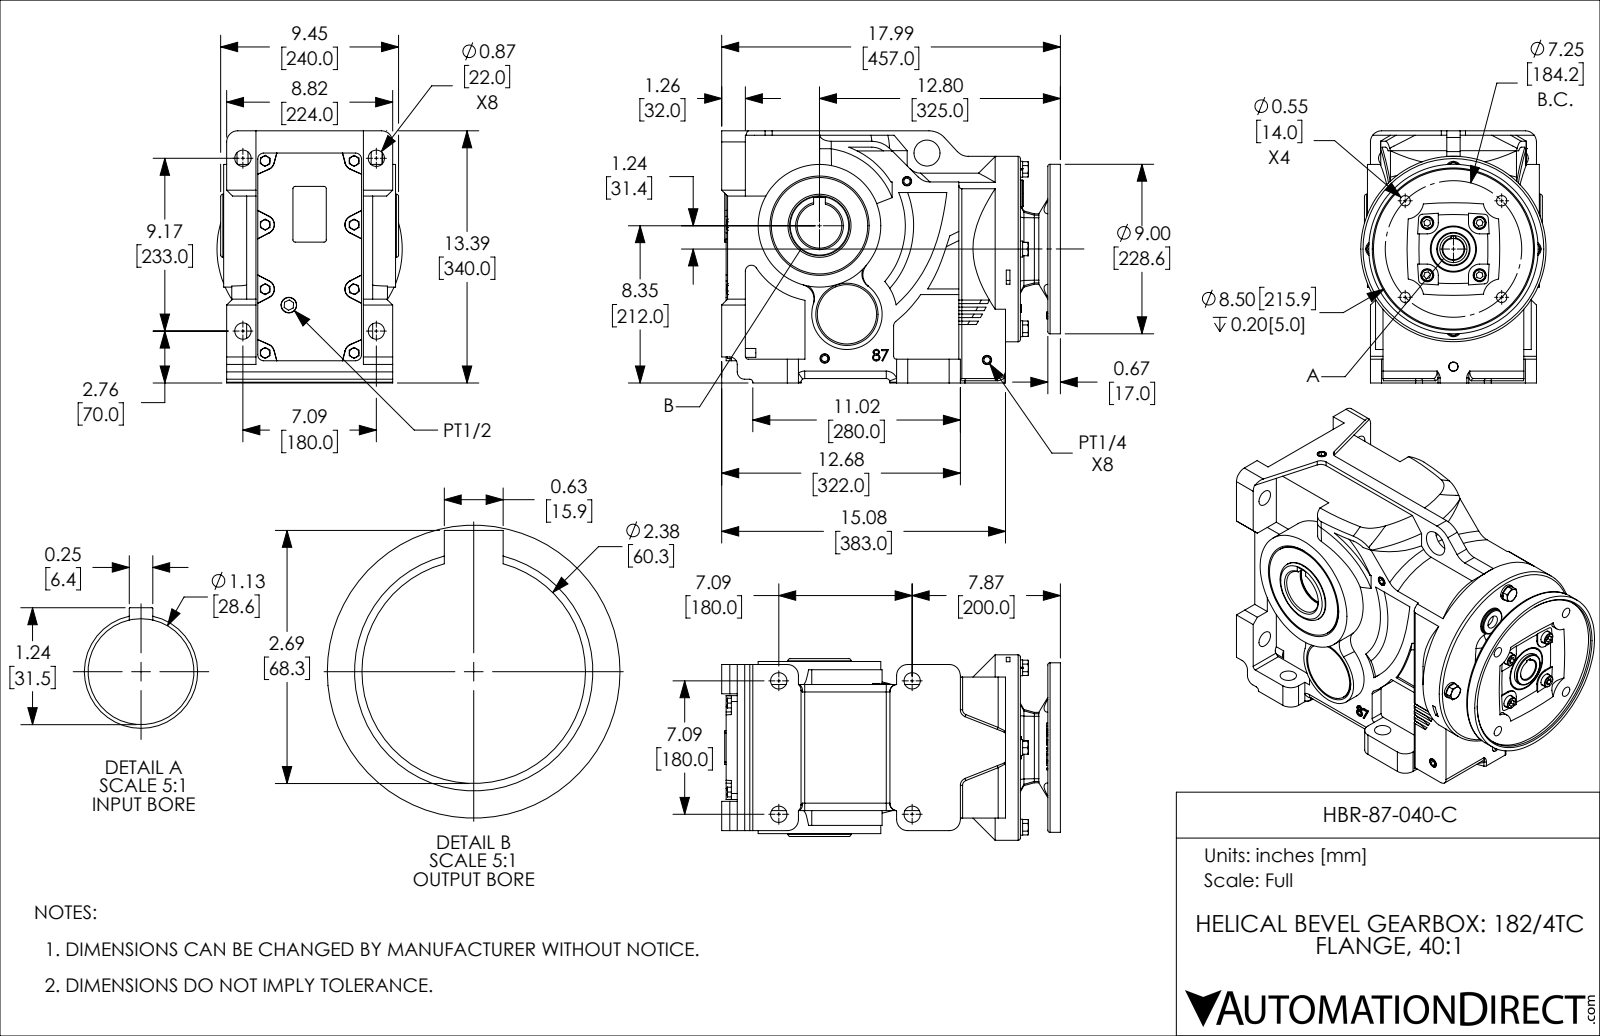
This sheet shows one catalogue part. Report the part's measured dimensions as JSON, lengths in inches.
{"part_name": "HBR-87-040-C", "step_written_by": "SolidWorks 2018 (AUTOMOTIVE_DESIGN)", "units": "inches", "bodies": {"solids": 8, "faces": 1111, "planar": 542, "cylindrical": 287, "other": 282}, "overall_size": [17.992, 13.501, 9.843], "volume_in3": 1396, "surface_area_in2": 1309, "round_holes": [[0.551, 8], [0.866, 8], [0.48, 4], [0.496, 4], [0.689, 4], [0.473, 1], [0.709, 1], [0.827, 1], [1.125, 1], [1.378, 1], [1.417, 1], [2.375, 1]], "round_bosses_or_shafts": [[0.846, 4], [0.63, 4], [0.472, 4], [9.843, 1], [9, 1], [6.513, 1], [5.118, 1], [3.346, 1]], "partial_cylinders_radius": [[0.394, 15], [0.591, 14], [0.157, 11], [0.118, 9], [0.315, 6], [0.689, 4], [0.984, 4], [19.528, 4]], "face_to_face_distances": [0.669, 0.236, 6.024, 1.063, 1.457, 7.087, 13.15, 0.394, 15.63, 1.22], "hole_center_spacings": [3.163, 7.087, 7.263, 2.784, 3.059, 4.125, 4.125, 4.232]}
